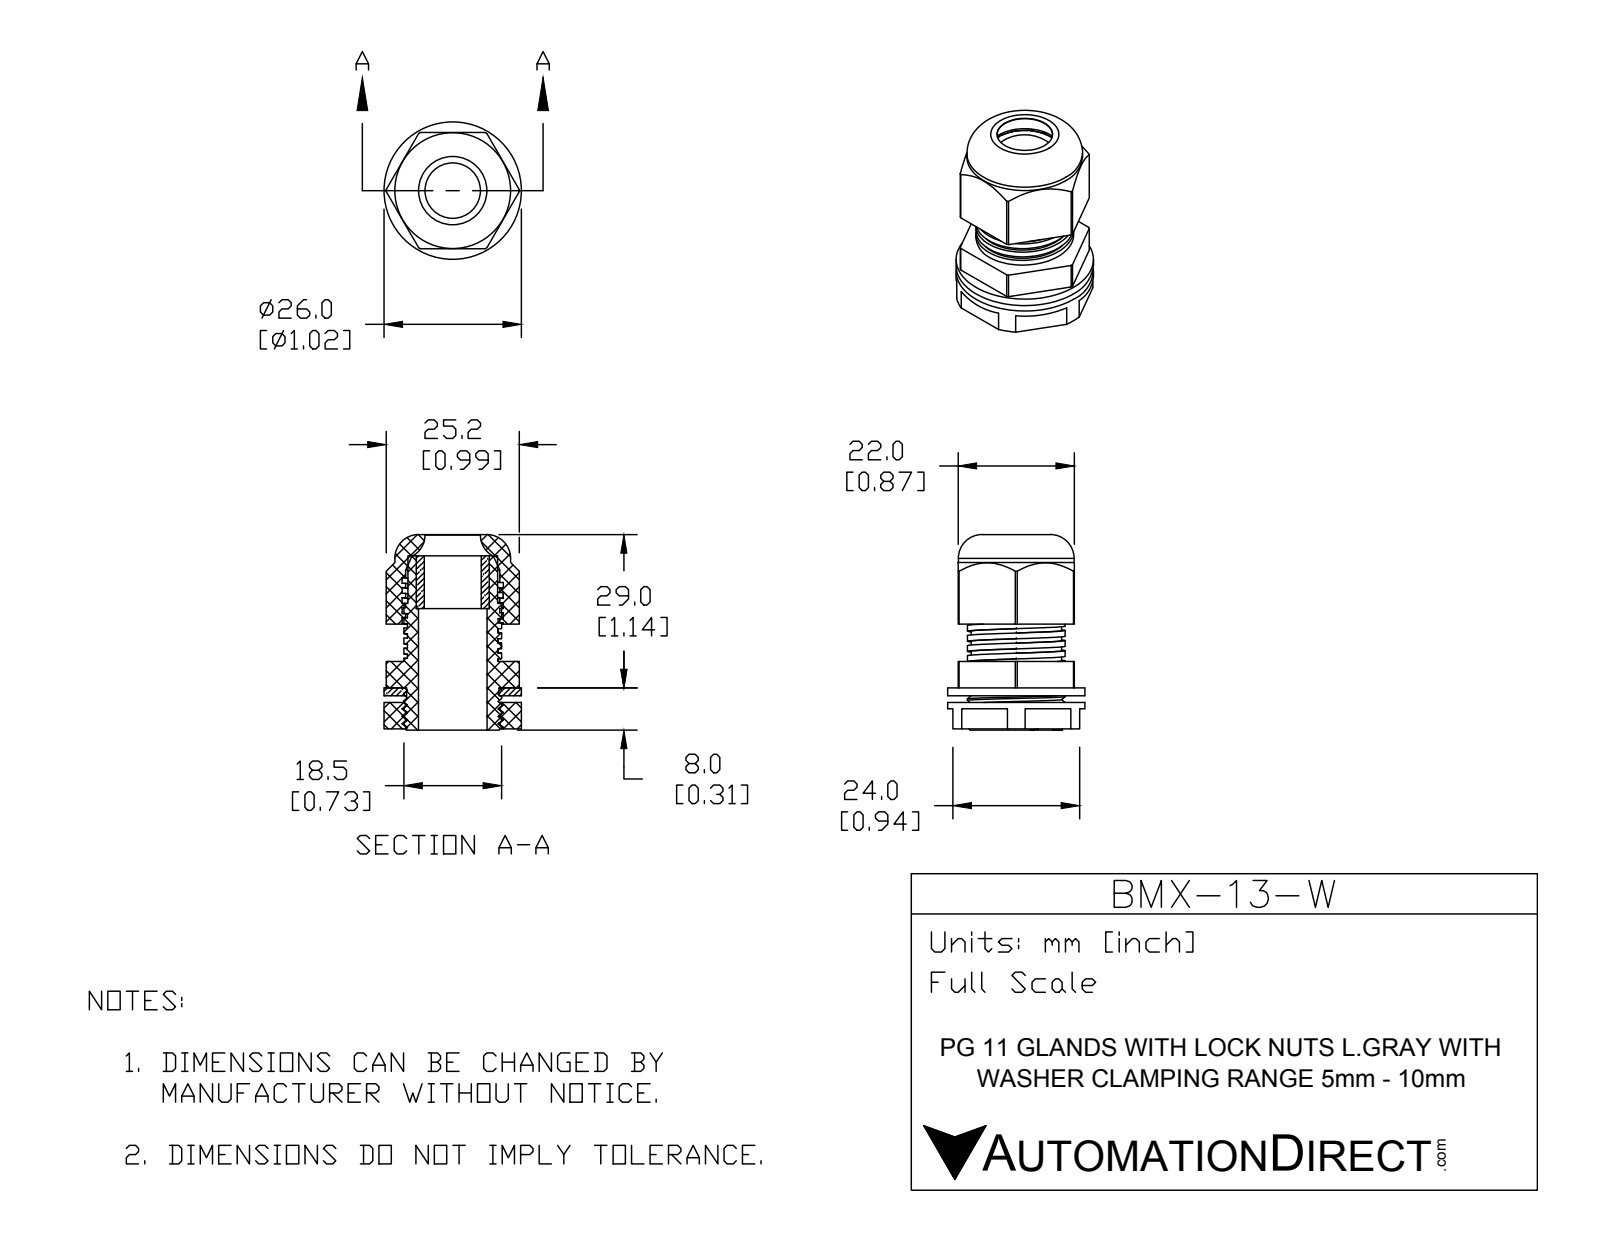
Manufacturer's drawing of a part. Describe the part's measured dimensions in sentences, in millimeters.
The part is named "BMX-13-W". Its 3-D file was written by "SolidWorks 2015 (CONFIG_CONTROL_DESIGN)". It is 5 solids with 197 faces: 99 planar, 76 cylindrical and 22 other. Overall it measures 37 by 26 by 26 millimeters. Its volume is 9 317 cubic millimeters and its surface area 10 584 square millimeters. Round holes: 1 of diameter 10.5, 1 of diameter 10.8, 1 of diameter 13, 1 of diameter 13.8, 1 of diameter 17.5, 1 of diameter 17.83. Round bosses or shafts: 1 of diameter 26, 1 of diameter 21.9, 1 of diameter 18.5, 1 of diameter 17. Partial cylindrical surfaces (rounded edges, fillets, slot ends): 1 of radius 12.6. The main face-to-face distances are 22, 5, 7.75, 23, 1.5, 6.5, 1, 1.25, 2.75, 6.25.
